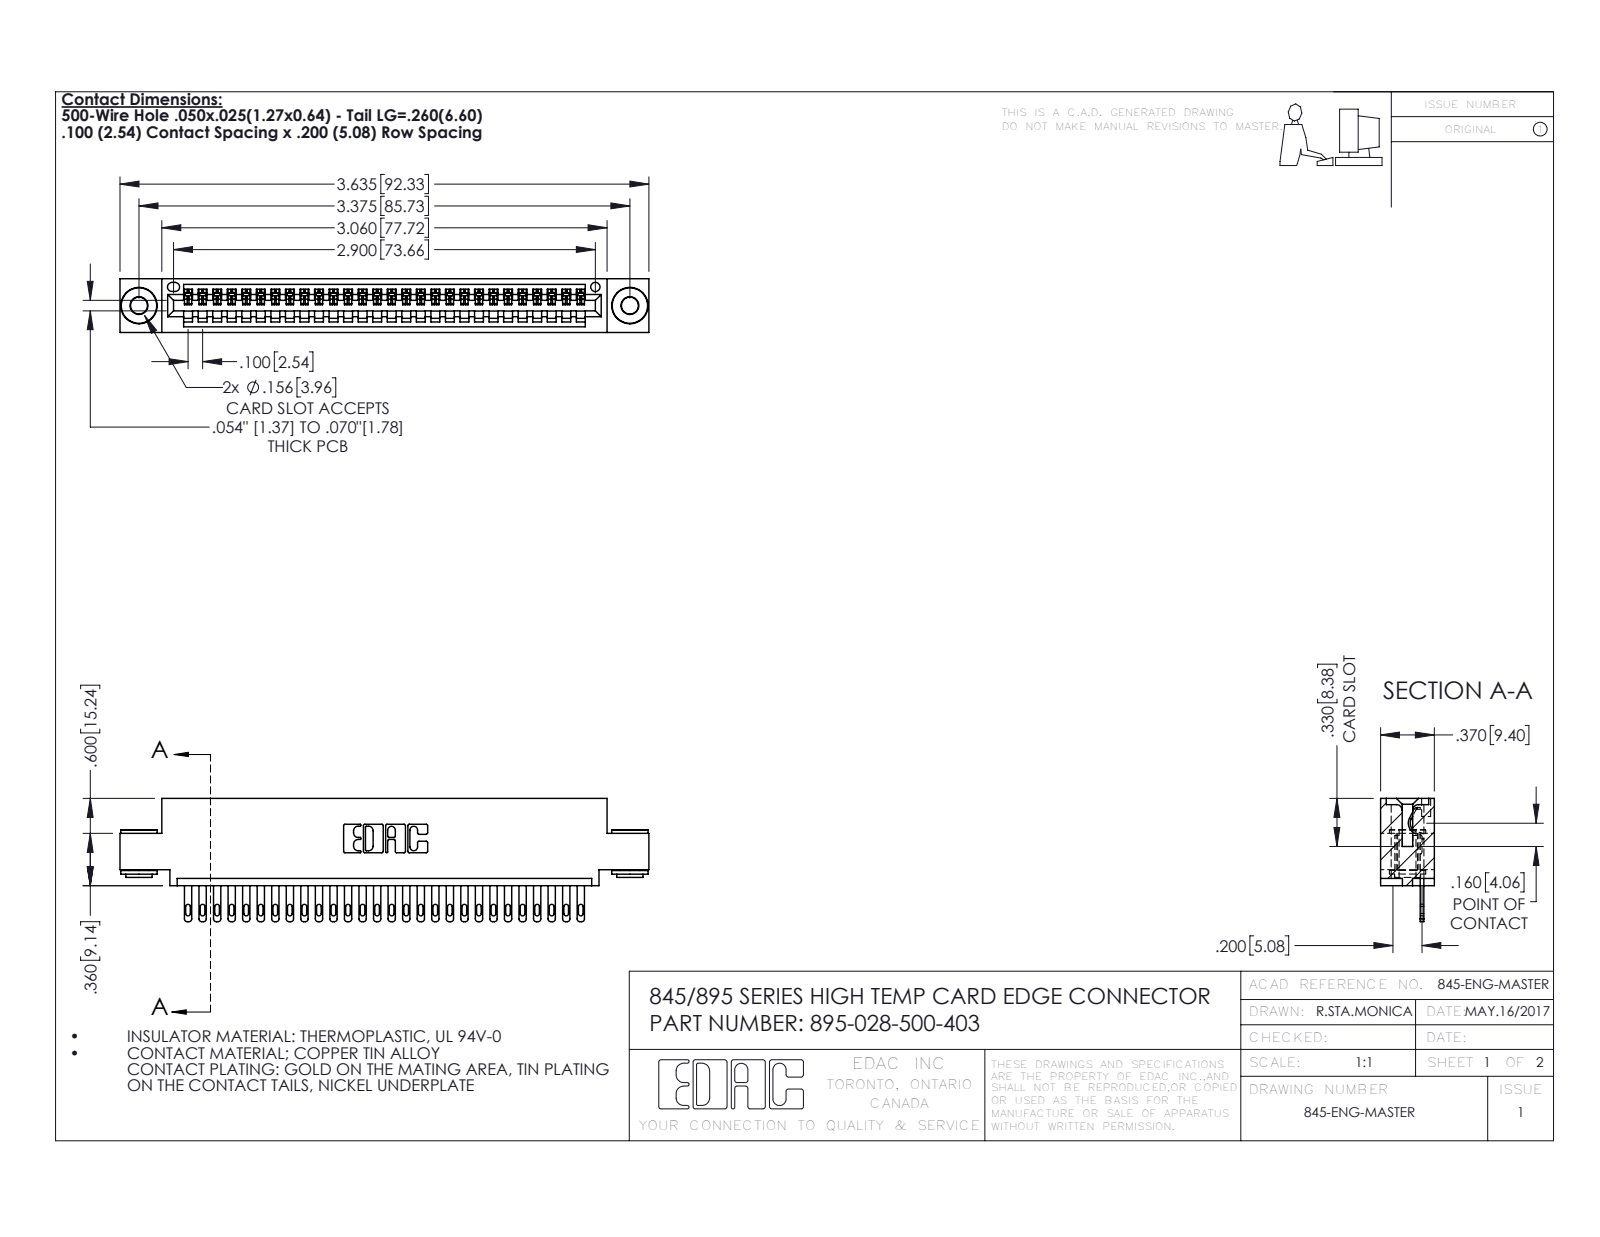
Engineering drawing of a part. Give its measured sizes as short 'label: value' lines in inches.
name: 345-250-002_345-250-002-102; 845 Part_0.110 Offset - 0.156 Dia-TH; 895-028-500-403; 345-292-001_345-293-100
written by: SolidWorks 2020 (CONFIG_CONTROL_DESIGN)
unit: in
bodies: 31 solids, 1680 faces (1046 planar, 626 cylindrical, 8 other)
size: 3.635 × 0.847 × 0.37
volume: 0.526 in³; area: 18.01 in²
holes: 2× ⌀0.116, 2× ⌀0.156, 1× ⌀0.064
bosses: 2× ⌀0.25, 2× ⌀0.18, 2× ⌀0.136
rounds: 56× R0.006, 56× R0.016, 56× R0.02, 22× R0.01, 6× R0.007, 6× R0.031, 3× R0.026, 2× R0.031
face distances: 0.072, 0.298, 0.37, 0.025, 0.2, 0.098, 0.272, 0.225, 0.149, 0.072
hole spacings: 0.27, 3.14, 3.375
